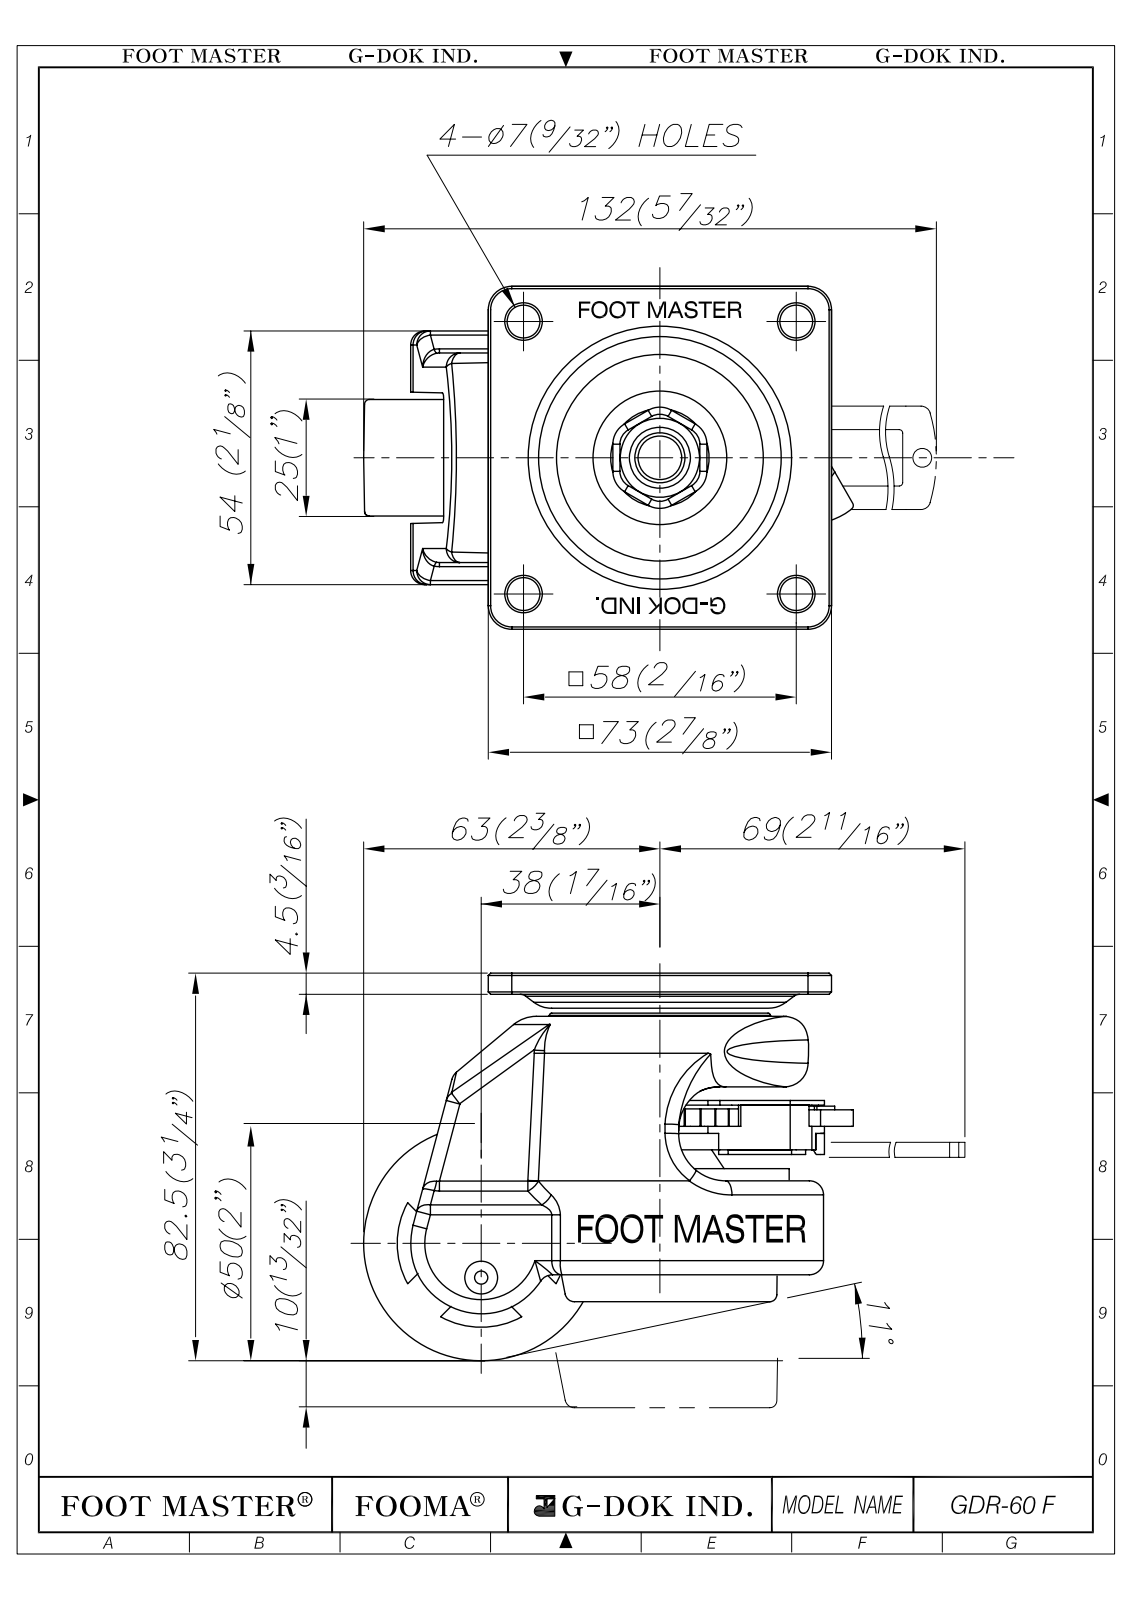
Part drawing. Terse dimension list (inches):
name: GDR-60F
written by: Autodesk Inventor 2009 (AUTOMOTIVE_DESIGN)
unit: in
bodies: 15 solids, 1322 faces (740 planar, 293 cylindrical, 289 other)
size: 4.016 × 3.228 × 2.874
holes: 6× ⌀0.276, 4× ⌀0.079, 2× ⌀0.083, 2× ⌀0.394, 1× ⌀0.138, 1× ⌀0.157, 1× ⌀0.161, 1× ⌀0.197, 1× ⌀0.331, 1× ⌀0.335, 1× ⌀0.386, 1× ⌀0.421
bosses: 4× ⌀0.138, 4× ⌀0.118, 2× ⌀0.122, 2× ⌀0.079, 1× ⌀1.535, 1× ⌀1.102, 1× ⌀1.063, 1× ⌀0.906
rounds: 46× R0.039, 23× R0.02, 20× R0.079, 14× R0.197, 4× R0.035, 2× R0.051, 2× R0.059, 2× R0.157
face distances: 0.177, 0.354, 0.945, 0.886, 0.591, 1.083, 0.157, 1.043, 0.571, 0.374
hole spacings: 1.615, 2.283, 0.341, 0.413, 0.652, 0.677, 0.699, 0.704
